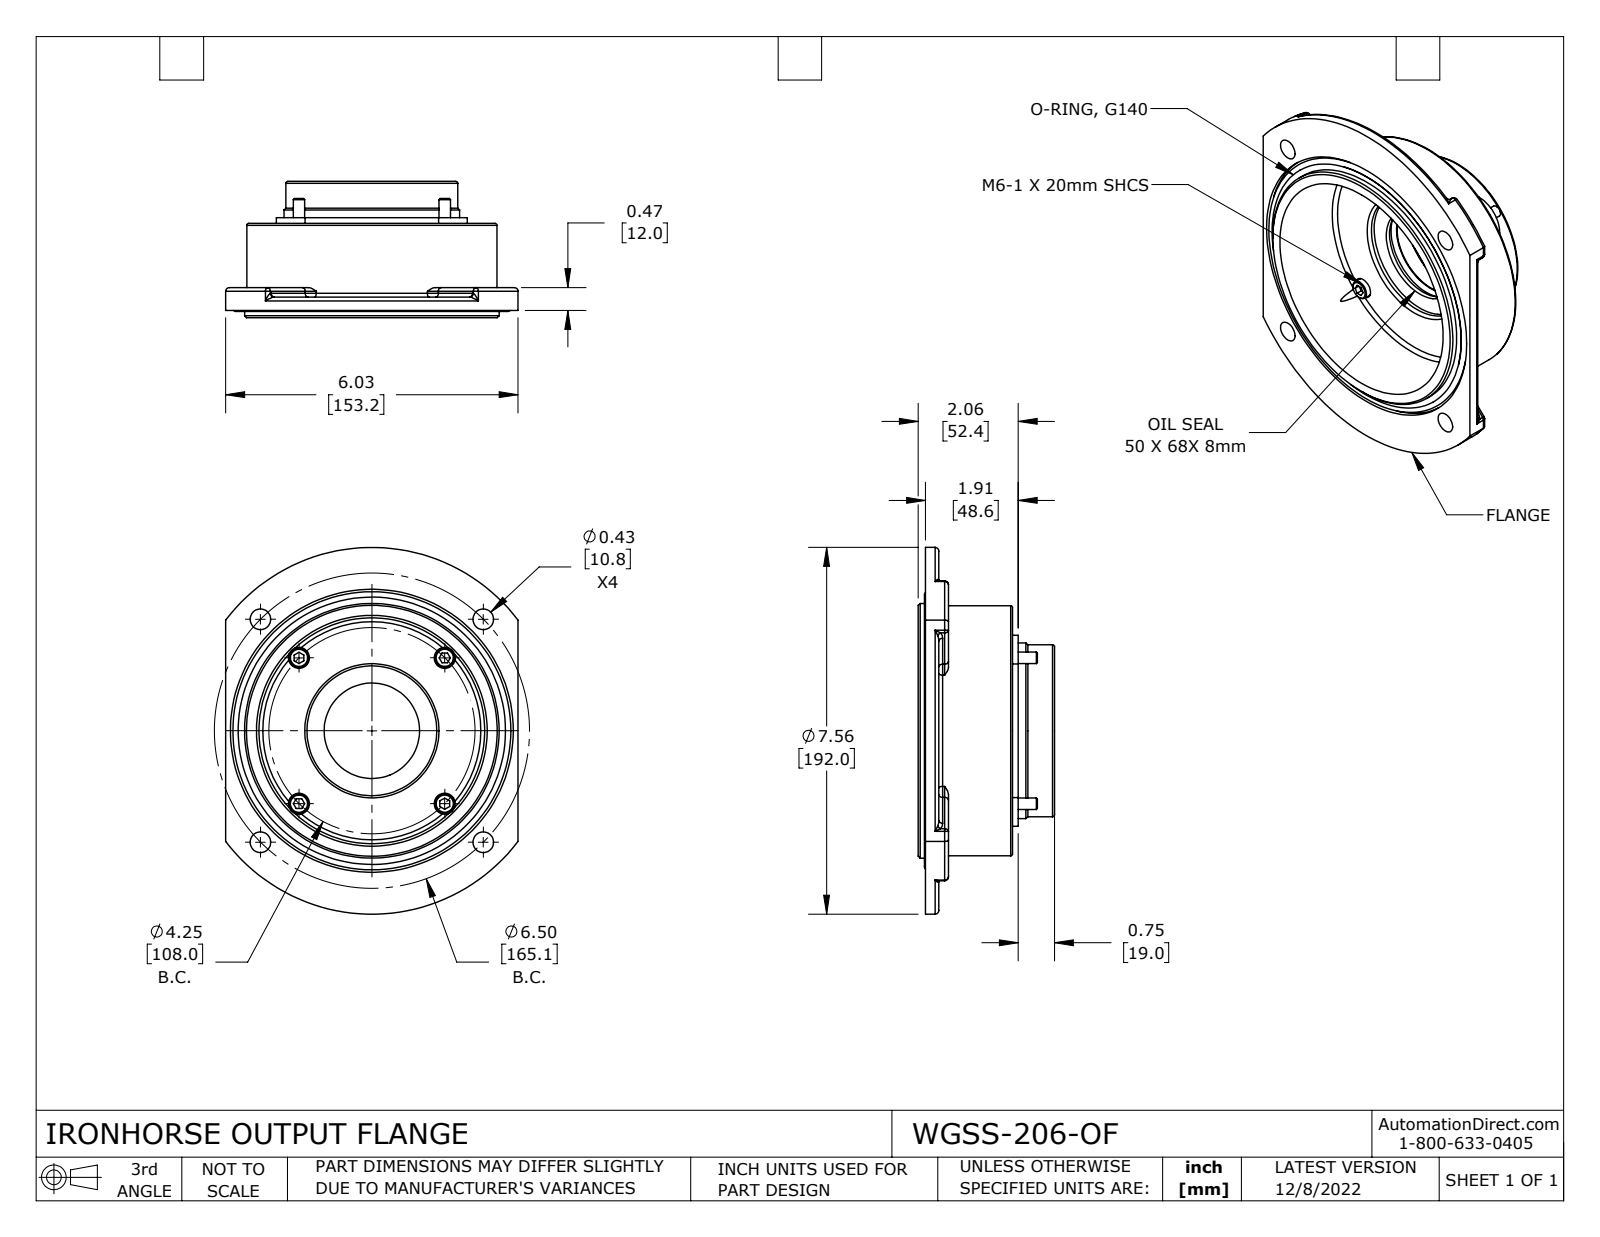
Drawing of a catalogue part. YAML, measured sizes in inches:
part_name: "WGSS-206-OF"
step_written_by: "SolidWorks 2021 (CONFIG_CONTROL_DESIGN)"
units: inches
bodies: {solids: 7, faces: 302, planar: 81, cylindrical: 116, other: 105}
overall_size: [7.56, 6.03, 2.811]
volume: 21.53
surface_area: 176.1
round_holes:
  - {diameter: 0.276, count: 4}
  - {diameter: 0.425, count: 4}
  - {diameter: 0.433, count: 4}
  - {diameter: 1.969, count: 1}
  - {diameter: 2.441, count: 1}
  - {diameter: 2.48, count: 1}
  - {diameter: 2.677, count: 1}
  - {diameter: 2.953, count: 1}
  - {diameter: 3.15, count: 1}
  - {diameter: 5.835, count: 1}
round_bosses_or_shafts:
  - {diameter: 0.394, count: 4}
  - {diameter: 0.236, count: 4}
  - {diameter: 5.512, count: 1}
  - {diameter: 5.25, count: 1}
  - {diameter: 5.157, count: 1}
  - {diameter: 3.622, count: 1}
  - {diameter: 3.543, count: 1}
  - {diameter: 2.205, count: 1}
partial_cylinders:
  - {radius: 0.079, count: 24}
  - {radius: 0.197, count: 8}
  - {radius: 0.591, count: 4}
  - {radius: 3.78, count: 1}
face_to_face_distances: [1.401, 0.276, 1.125, 0.394, 0.472, 0.118, 0.197, 1.519, 1.637, 0.157]
hole_center_spacings: [3.883, 1.124, 2.126, 3.006, 3.25, 4.596, 5.376, 4.252]
